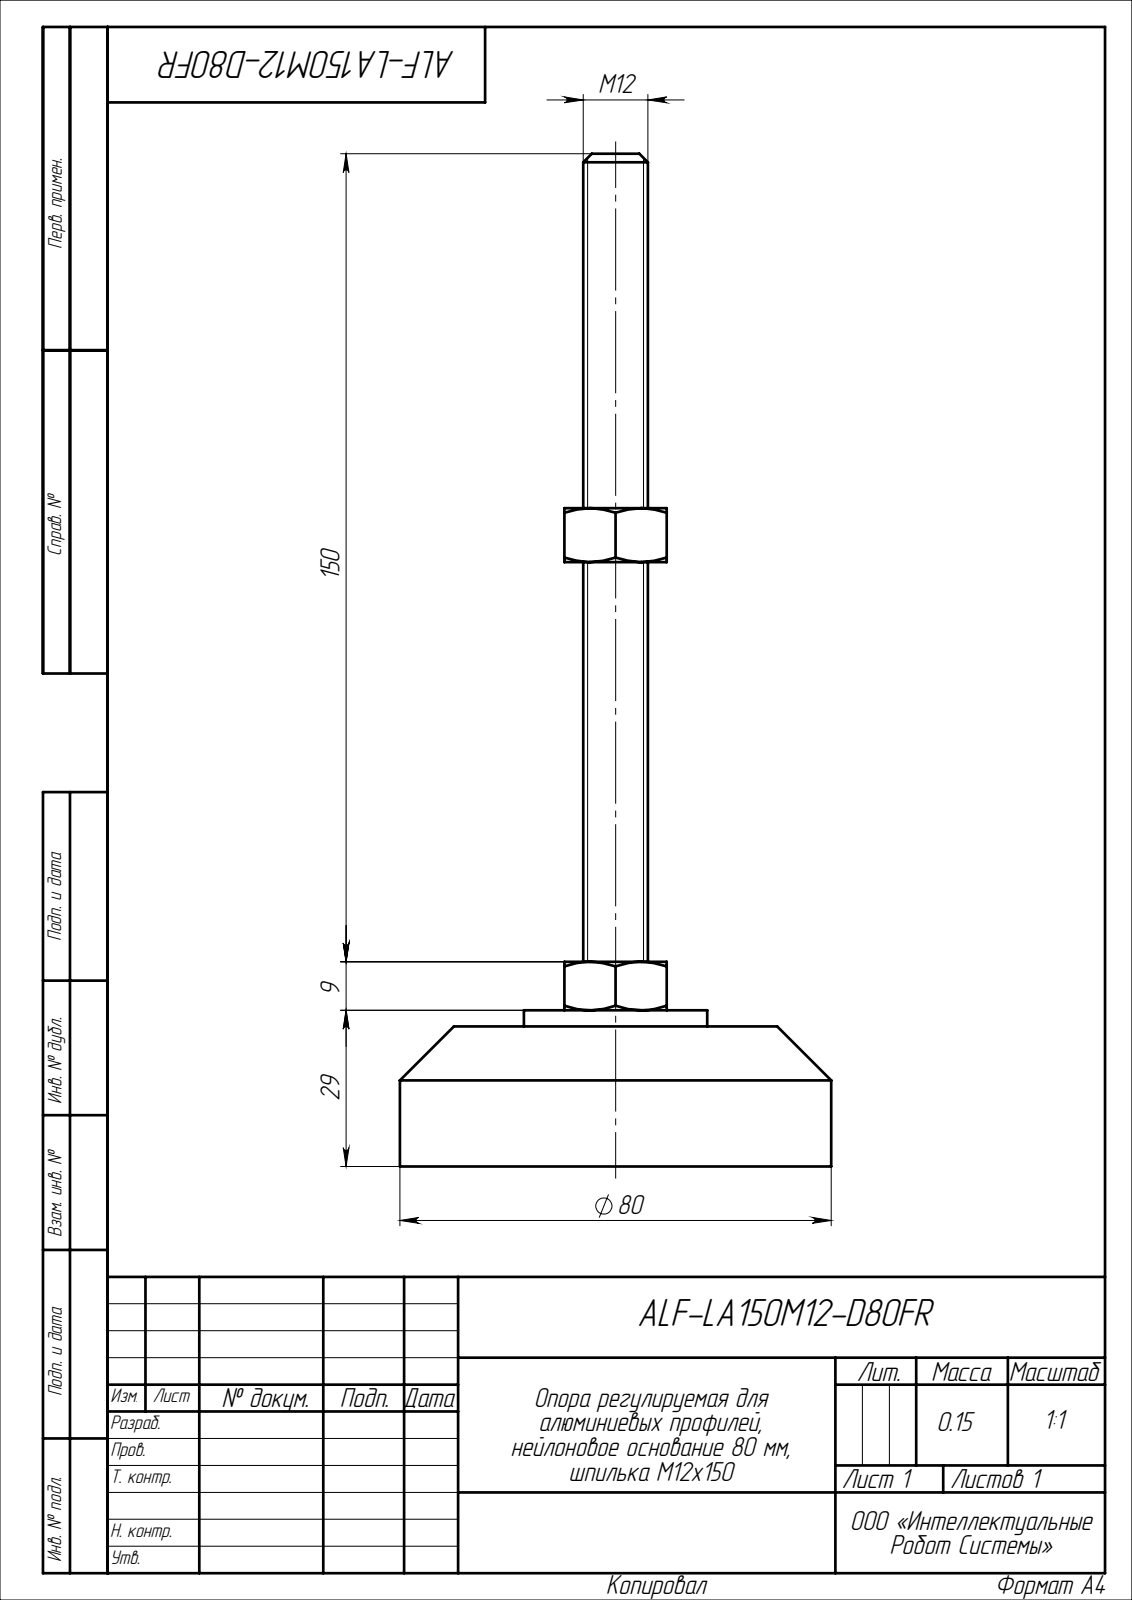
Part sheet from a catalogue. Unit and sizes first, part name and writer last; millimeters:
Units: millimetres
Overall size (bounding box): 188 × 80 × 80
Round bosses / shafts (diameter × count): ⌀80 ×1, ⌀34 ×1, ⌀12 ×1
Main face-to-face distances: 26, 29, 3, 19, 38, 12, 9, 122.2, 96.2, 93.2
Volume: 143 595 mm³ · Surface area: 22 194 mm²
Bodies: 1 solid, 55 faces (19 planar, 8 cylindrical, 28 other)
Part name (STEP PRODUCT): ALF-LA150M12-D80FR
STEP written by: SolidWorks 2022 (CONFIG_CONTROL_DESIGN)
